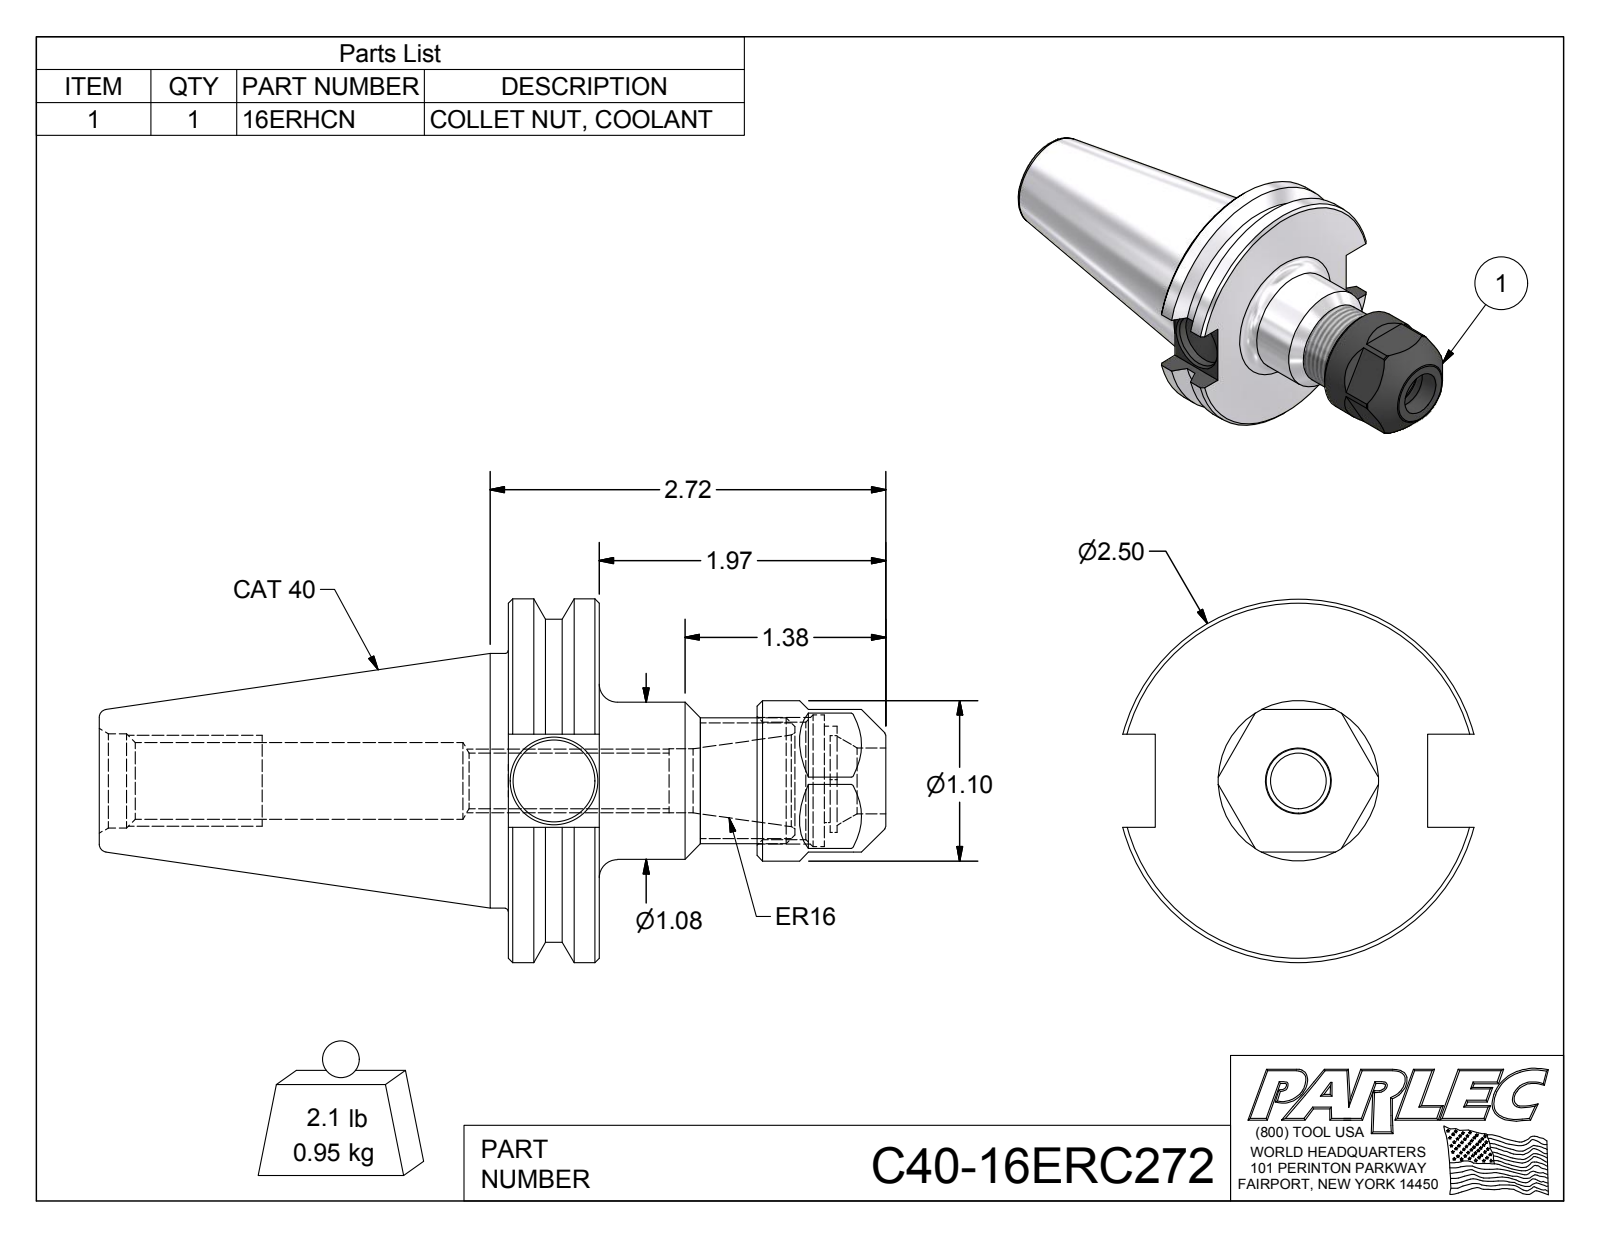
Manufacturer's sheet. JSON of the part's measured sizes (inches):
{"part_name": "C40-16ER2-1; 16ERHCN; C40-16ERC272", "step_written_by": "Autodesk Inventor 2016 (AUTOMOTIVE_DESIGN)", "units": "inches", "bodies": {"solids": 2, "faces": 81, "planar": 28, "cylindrical": 20, "other": 33}, "overall_size": [5.407, 2.5, 2.417], "volume_in3": 7.37, "surface_area_in2": 42.3, "round_holes": [[0.383, 1], [0.44, 1], [0.453, 1], [0.527, 1], [0.563, 1], [0.648, 1], [0.661, 1], [0.807, 1], [0.906, 1]], "round_bosses_or_shafts": [[2.5, 1], [2.219, 1], [1.75, 1], [1.102, 1], [1.08, 1], [0.866, 1]], "partial_cylinders_radius": [[0.354, 1]], "face_to_face_distances": [0.625, 0.979, 0.169, 0.809, 2.174, 1.549, 0.64, 1.709, 1.084, 0.465], "hole_center_spacings": [0.051]}
